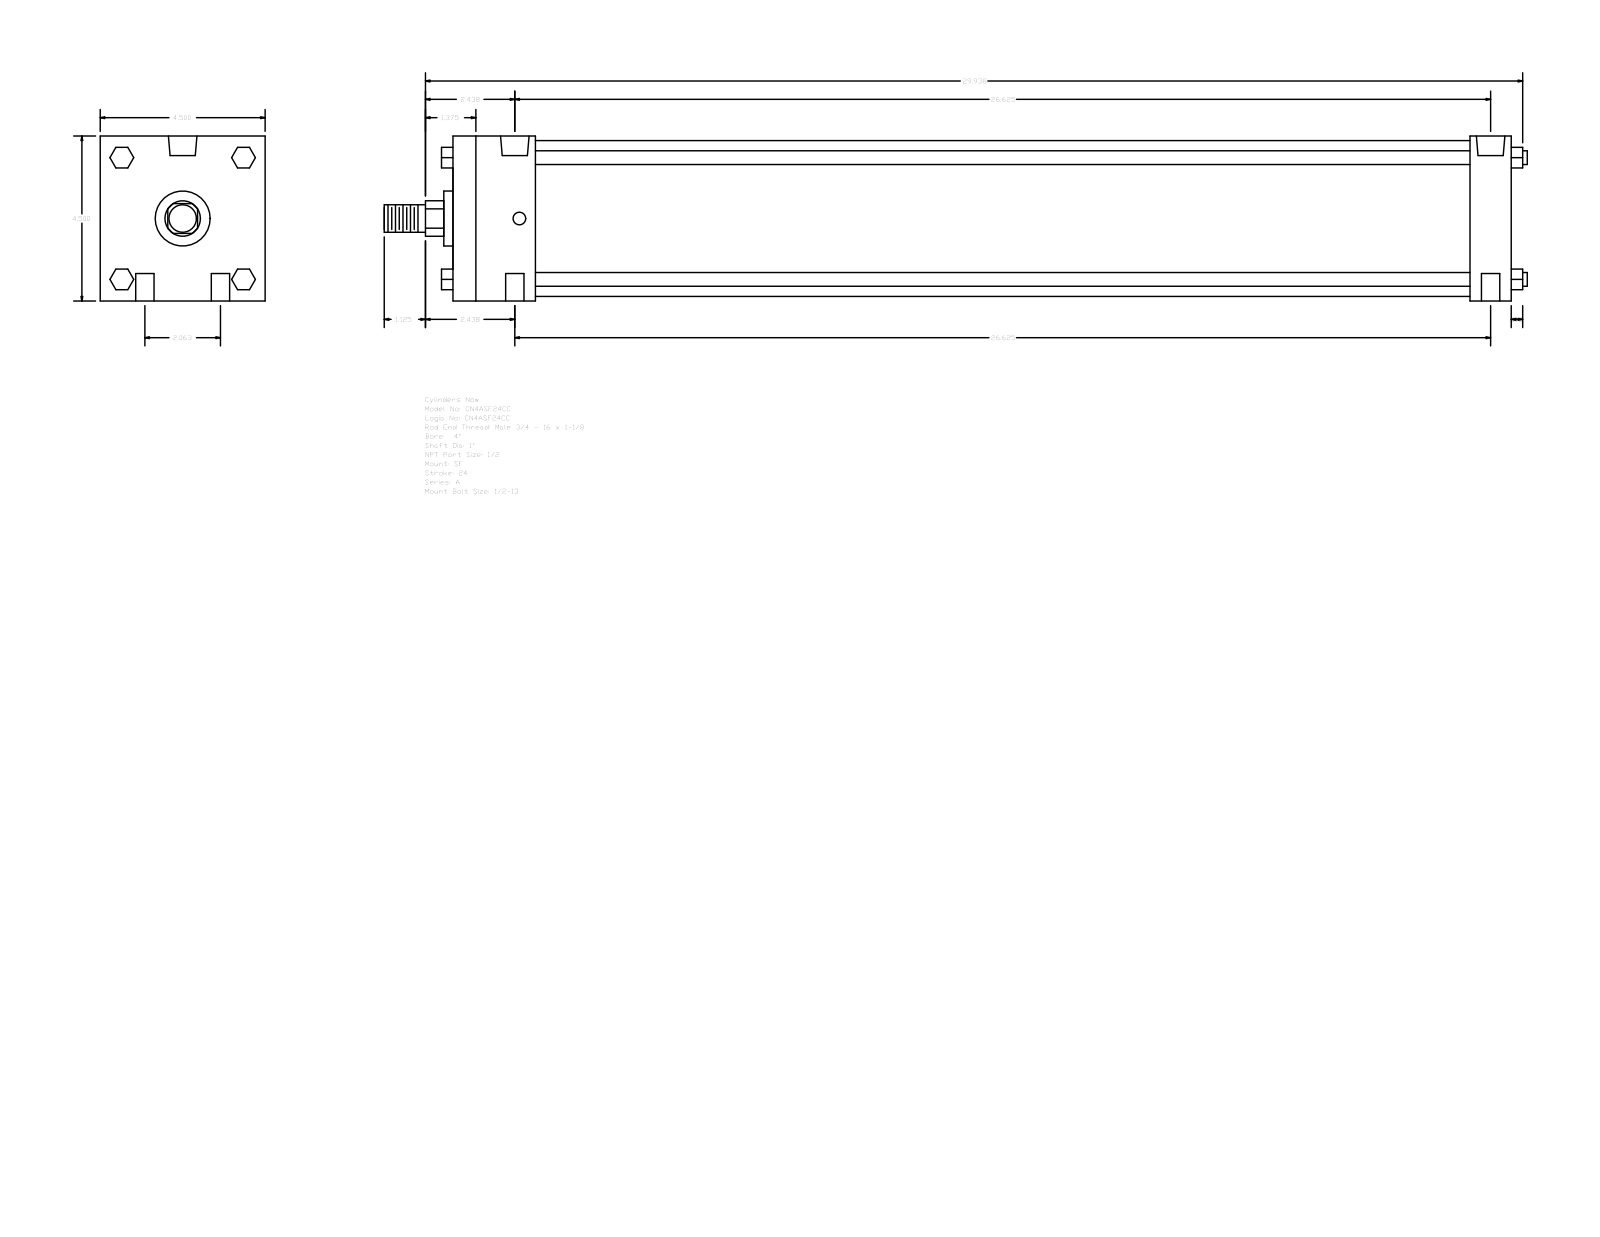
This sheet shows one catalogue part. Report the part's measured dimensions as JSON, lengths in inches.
{"part_name": "A_SF__0400_1", "step_written_by": "GSSL Pune (CONFIG_CONTROL_DESIGN)", "units": "inches", "bodies": {"solids": 0, "faces": 124, "planar": 94, "cylindrical": 30, "other": 0}, "overall_size": [31.187, 4.5, 4.5], "round_holes": [[0.5, 4], [0.344, 2], [0.778, 2]], "round_bosses_or_shafts": [[0.375, 4], [4.25, 1], [1.5, 1], [1, 1], [0.75, 1]], "partial_cylinders_radius": [[0.484, 1]], "face_to_face_distances": [4.5, 28.875, 27.75, 1.125, 2.25, 25.5, 26.625, 0.563, 1.66, 2.875], "hole_center_spacings": [1.031, 26.645, 26.625, 2.062, 26.705, 26.375]}
